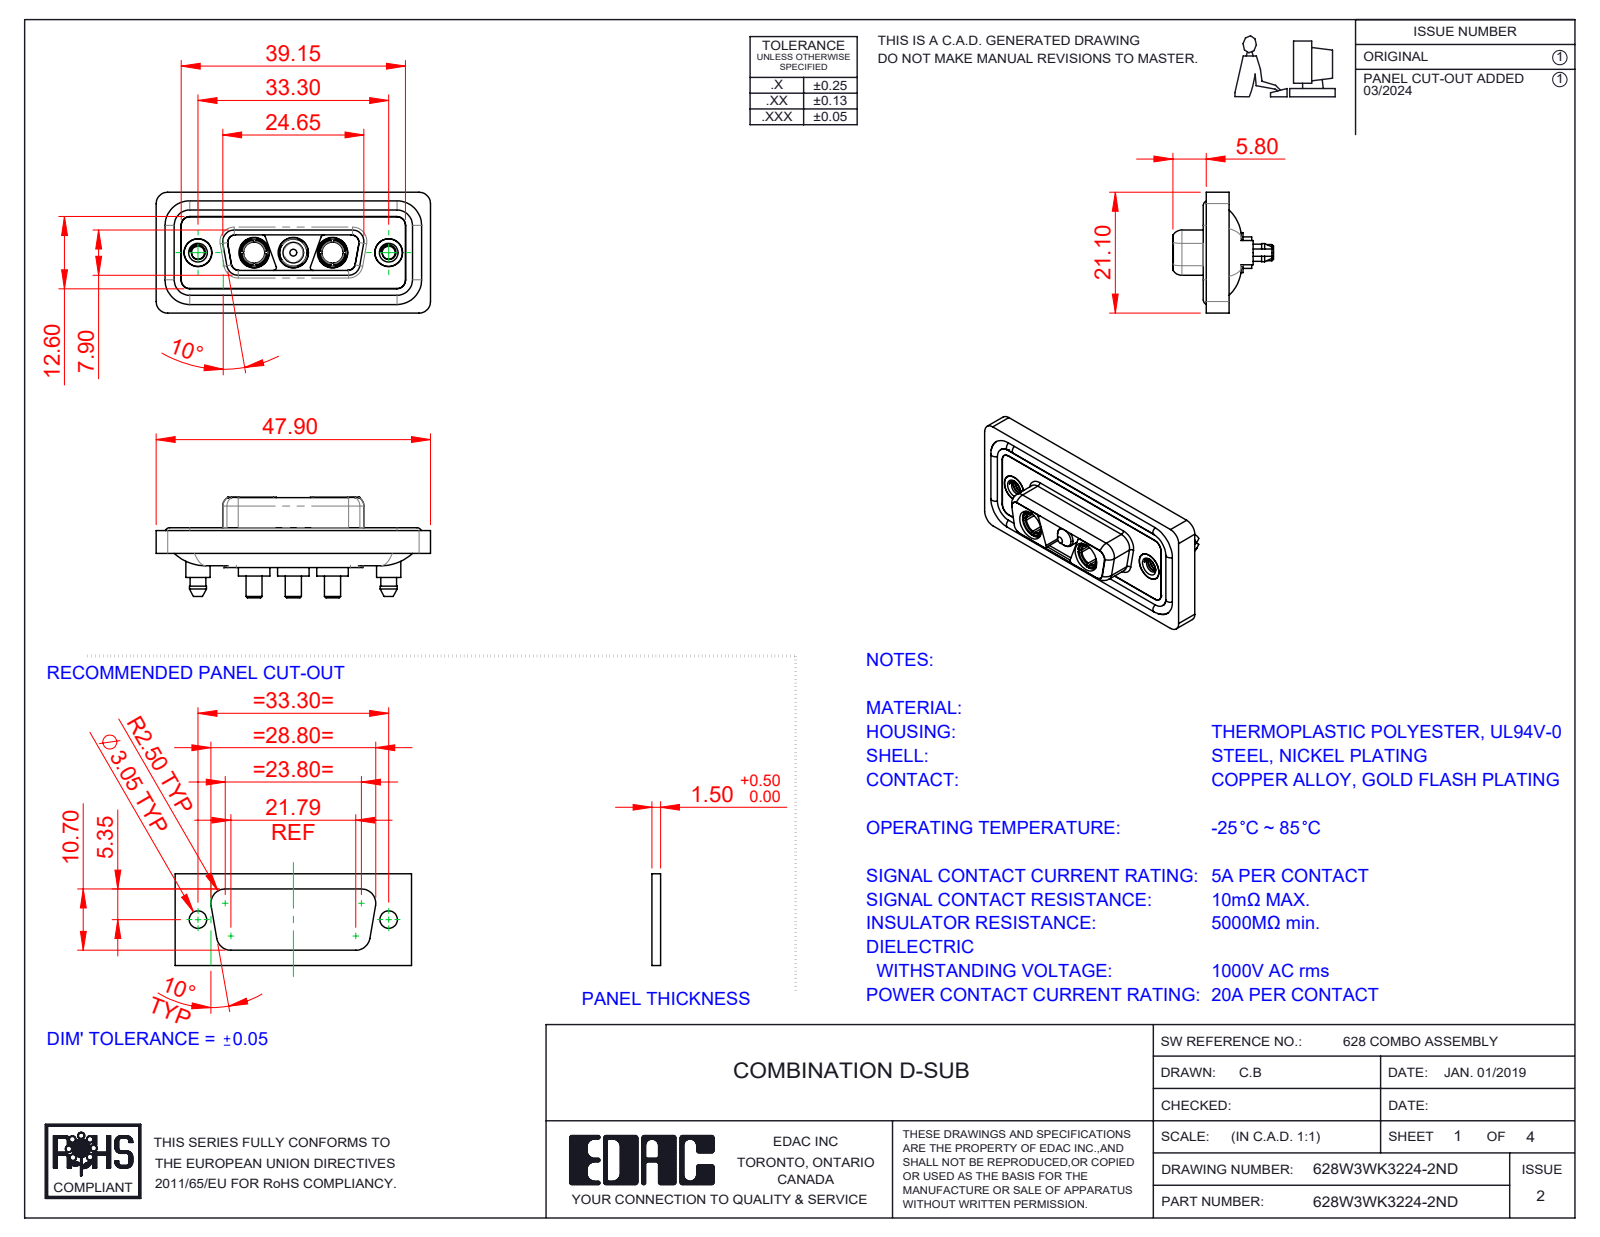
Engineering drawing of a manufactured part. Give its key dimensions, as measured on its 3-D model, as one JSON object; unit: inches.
{"part_name": "628Combo Shell Rear_15 Contacts; 628Combo Housing_3WK3; 628W3WK3224-2ND; 628Combo Waterproof Housing_15 Contacts (+4 more)", "step_written_by": "SolidWorks 2023 (CONFIG_CONTROL_DESIGN)", "units": "inches", "bodies": {"solids": 13, "faces": 649, "planar": 194, "cylindrical": 306, "other": 149}, "overall_size": [1.886, 0.831, 0.691], "volume_in3": 0.367, "surface_area_in2": 15.26, "round_holes": [[0.191, 5], [0.209, 3], [0.089, 2], [0.146, 2], [0.157, 2], [0.159, 2], [0.197, 2]], "round_bosses_or_shafts": [[0.063, 4], [0.217, 3], [0.205, 3], [0.187, 3], [0.148, 3], [0.11, 3], [0.213, 2], [0.195, 2]], "partial_cylinders_radius": [[0.059, 24], [0.079, 20], [0.053, 12], [0.063, 10], [0.02, 8], [0.01, 4], [0.024, 4], [0.026, 4]], "face_to_face_distances": [0.016, 0.063, 0.071, 0.02, 0.043, 0.114, 0.222, 0.278, 0.059, 0.211], "hole_center_spacings": [0.27, 0.386, 0.656, 0.925, 0.539, 1.311]}
